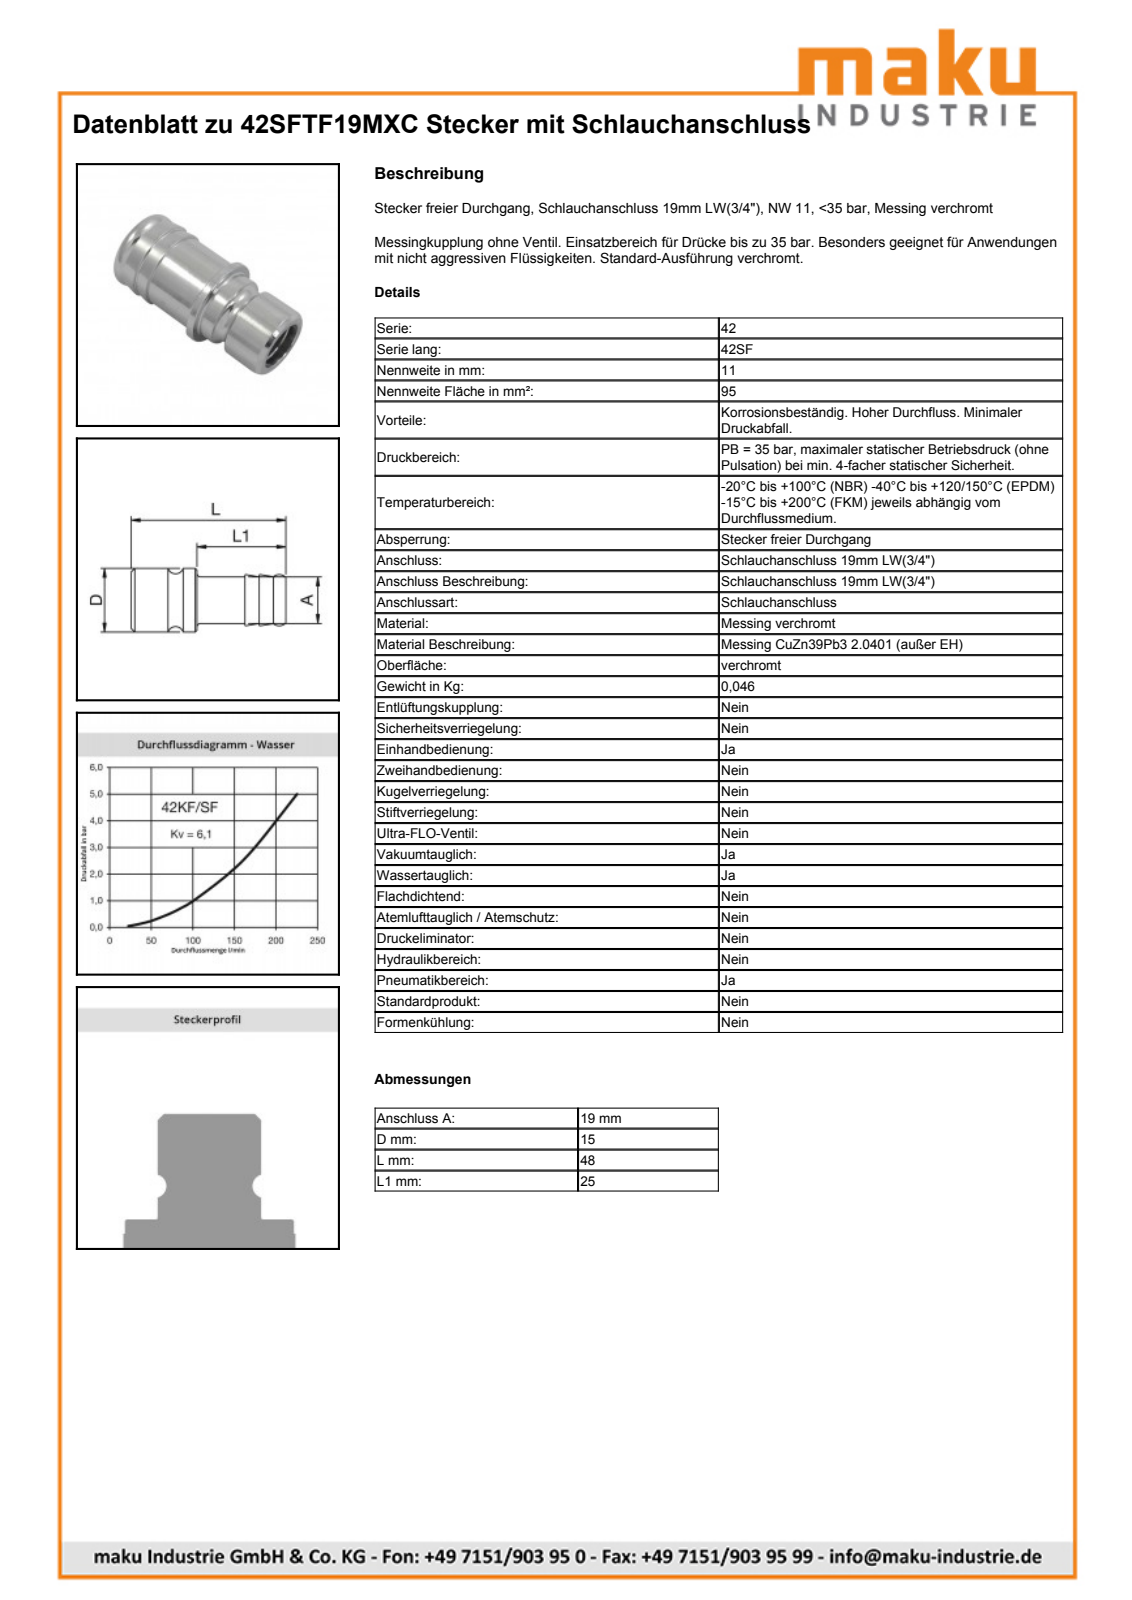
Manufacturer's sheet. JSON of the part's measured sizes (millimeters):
{"part_name": "D103468", "step_written_by": "Autodesk Inventor 2011 (AUTOMOTIVE_DESIGN)", "units": "millimeters", "bodies": {"solids": 1, "faces": 27, "planar": 6, "cylindrical": 7, "other": 14}, "overall_size": [45.5, 22, 22], "volume_mm3": 5601, "surface_area_mm2": 5221, "round_holes": [[11, 1], [12.2, 1], [16, 1]], "round_bosses_or_shafts": [[22, 1], [19.1, 1], [17.9, 1]], "face_to_face_distances": [18.5, 45.5, 27, 34, 15.5, 11.5, 2.6, 15.9, 31.4, 42.9]}
